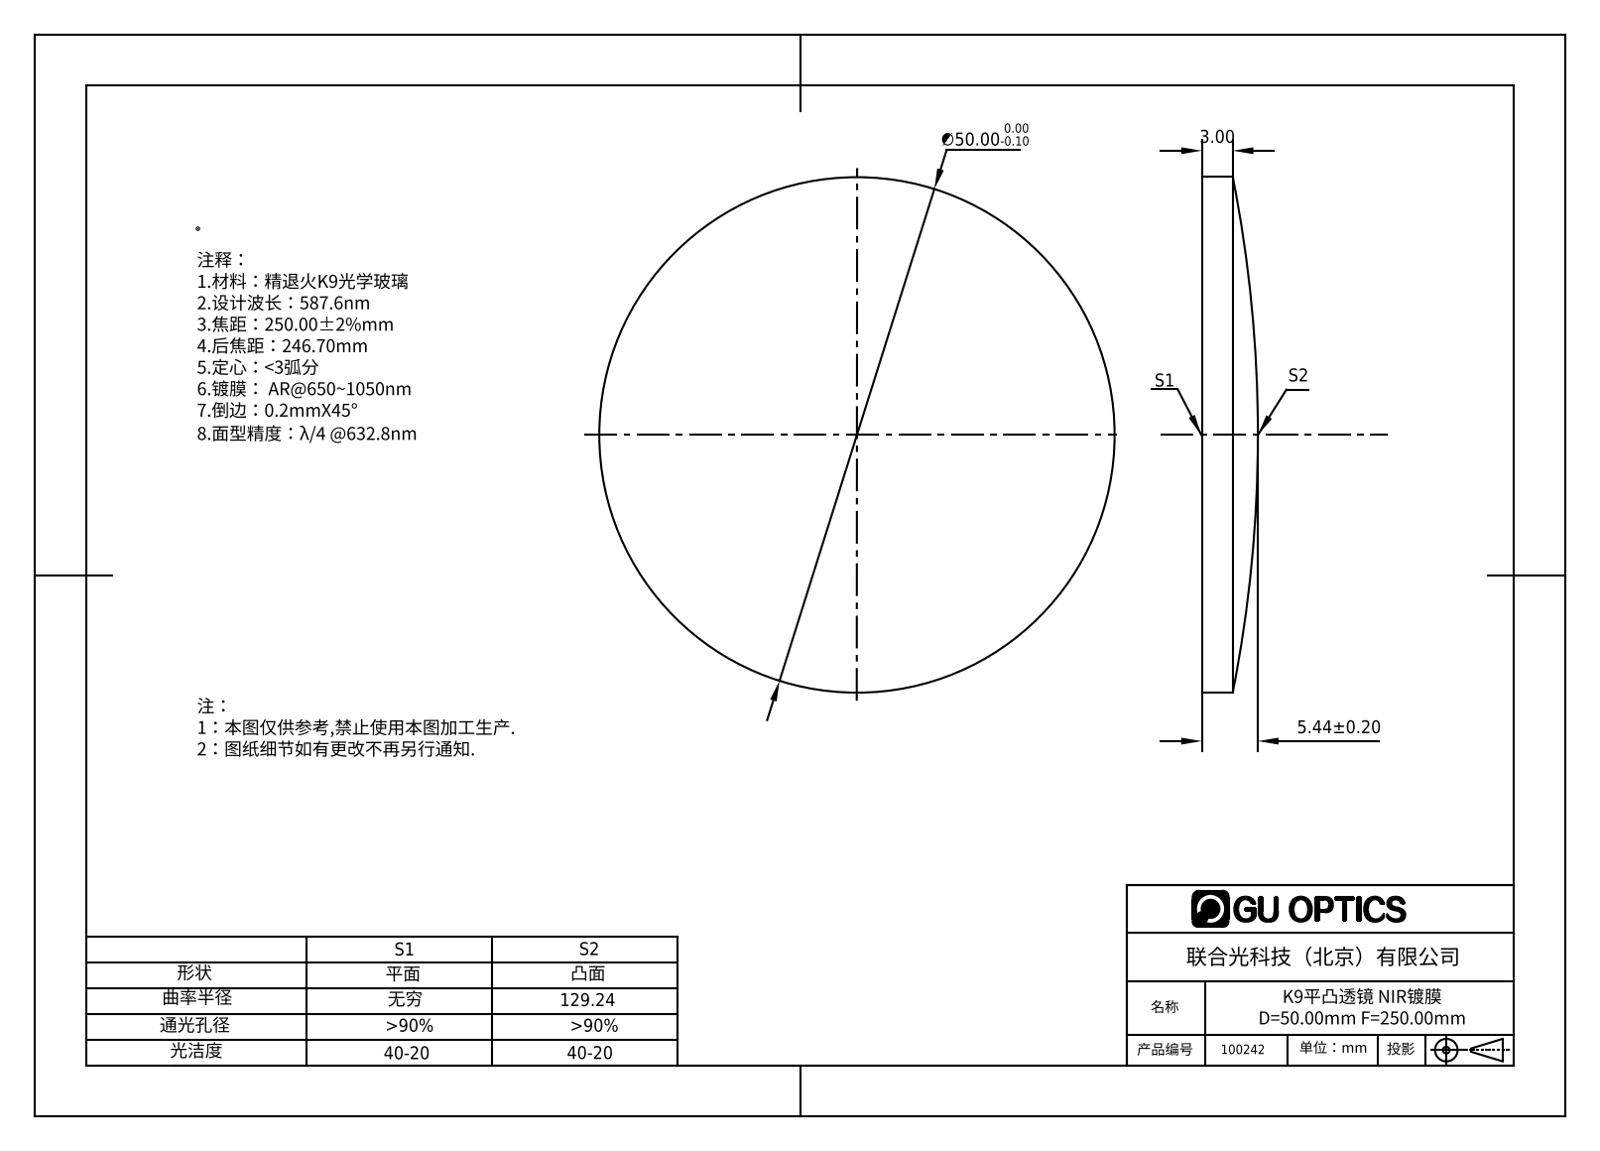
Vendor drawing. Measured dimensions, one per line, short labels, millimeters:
name: 100242
written by: SolidWorks 2016 (AUTOMOTIVE_DESIGN)
unit: mm
bodies: 1 solid, 5 faces (1 planar, 2 cylindrical, 2 other)
size: 50 × 50 × 5.44
volume: 8 294 mm³; area: 4 417 mm²
bosses: 1× ⌀50
